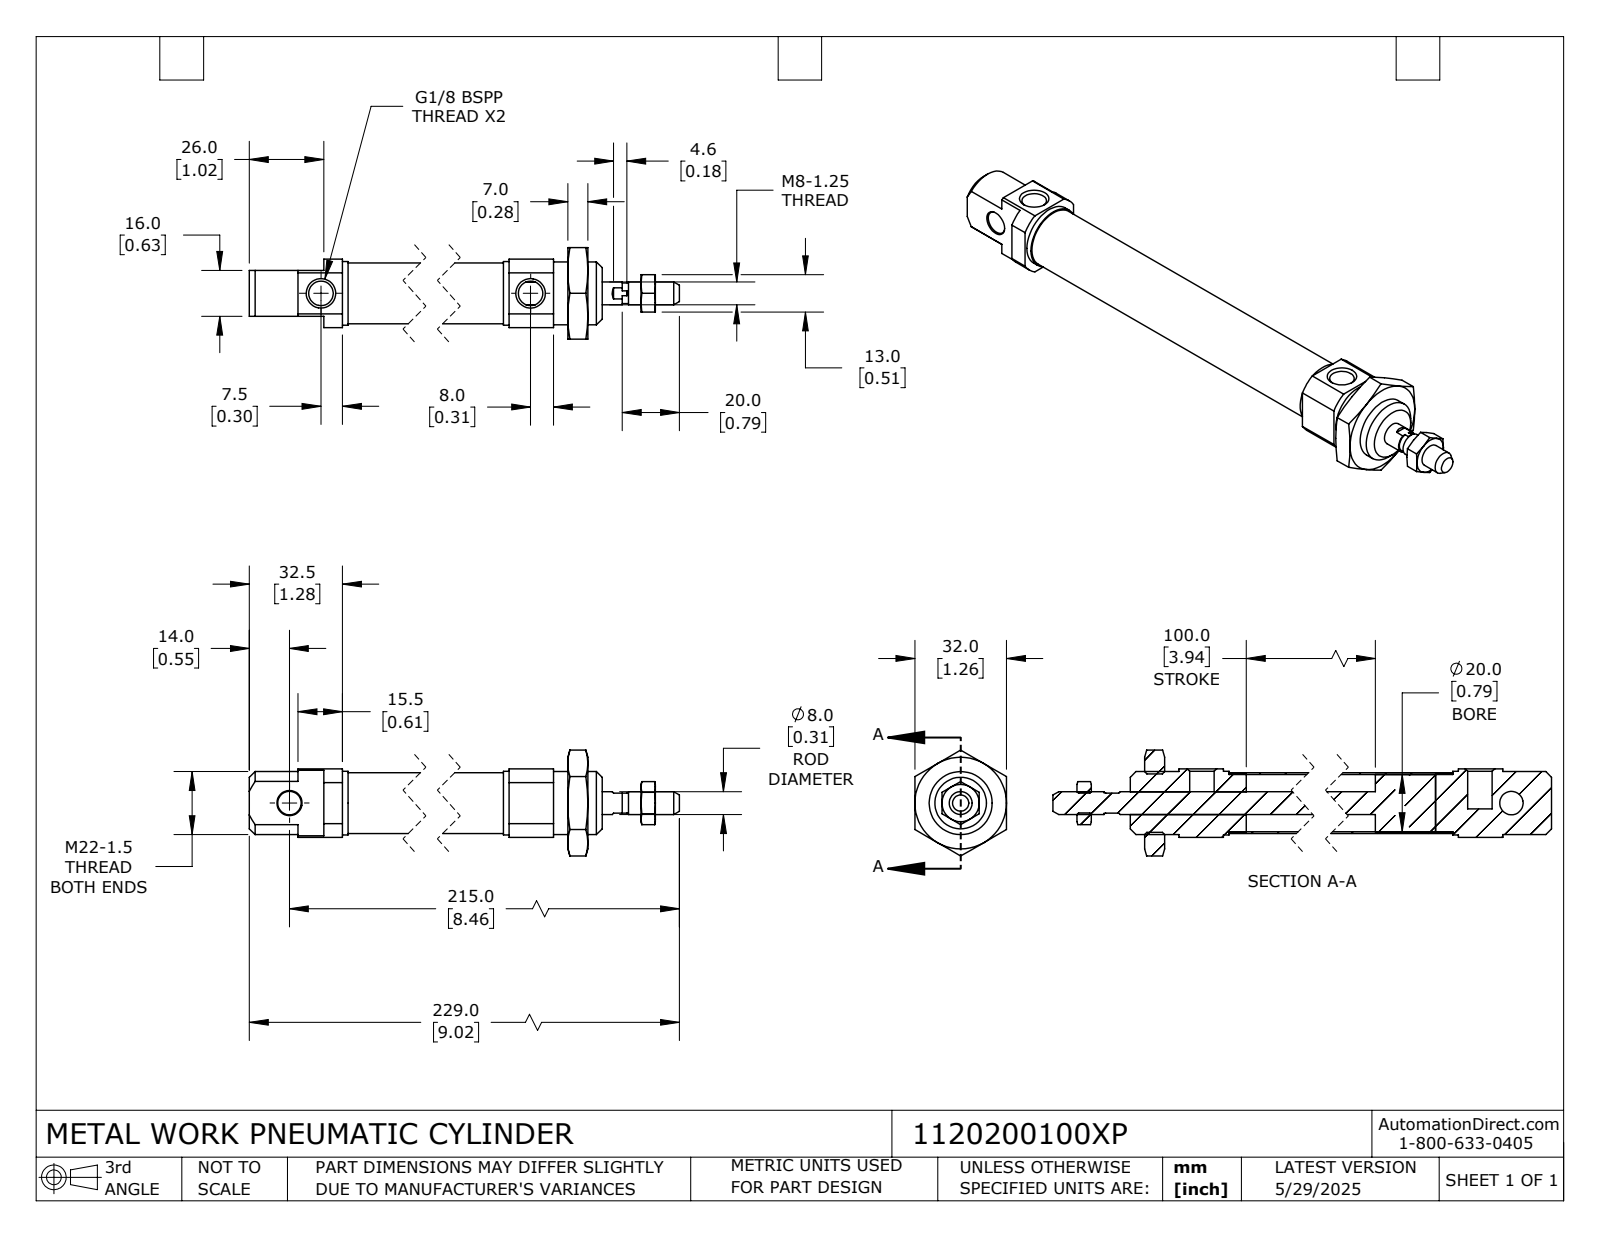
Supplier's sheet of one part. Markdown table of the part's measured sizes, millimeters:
| quantity | value |
| --- | --- |
| part name | 1120200100XP; 1120200100XP_ROD; 1120200100XP_BODY |
| STEP written by | SolidWorks 2024 (CONFIG_CONTROL_DESIGN) |
| units | millimeters |
| bodies | 6 solids, 147 faces (56 planar, 45 cylindrical, 46 other) |
| overall size | 229 × 36.95 × 32 |
| volume | 52 848 mm³ |
| surface area | 35 841 mm² |
| round holes (diameter × count) | 8.57 × 2, 6.92 × 1, 8.2 × 1, 20 × 1, 20.38 × 1 |
| round bosses / shafts (diameter × count) | 22.2 × 1, 22 × 1, 21.27 × 1, 20.15 × 1, 8 × 1, 7.2 × 1 |
| partial cylindrical surfaces (radius × count) | 13.95 × 1 |
| main face-to-face distances | 3.97, 19.97, 23.94, 8, 40.5, 161.5, 7, 5, 156.5, 149.5 |
| hole center spacings | 152 |
